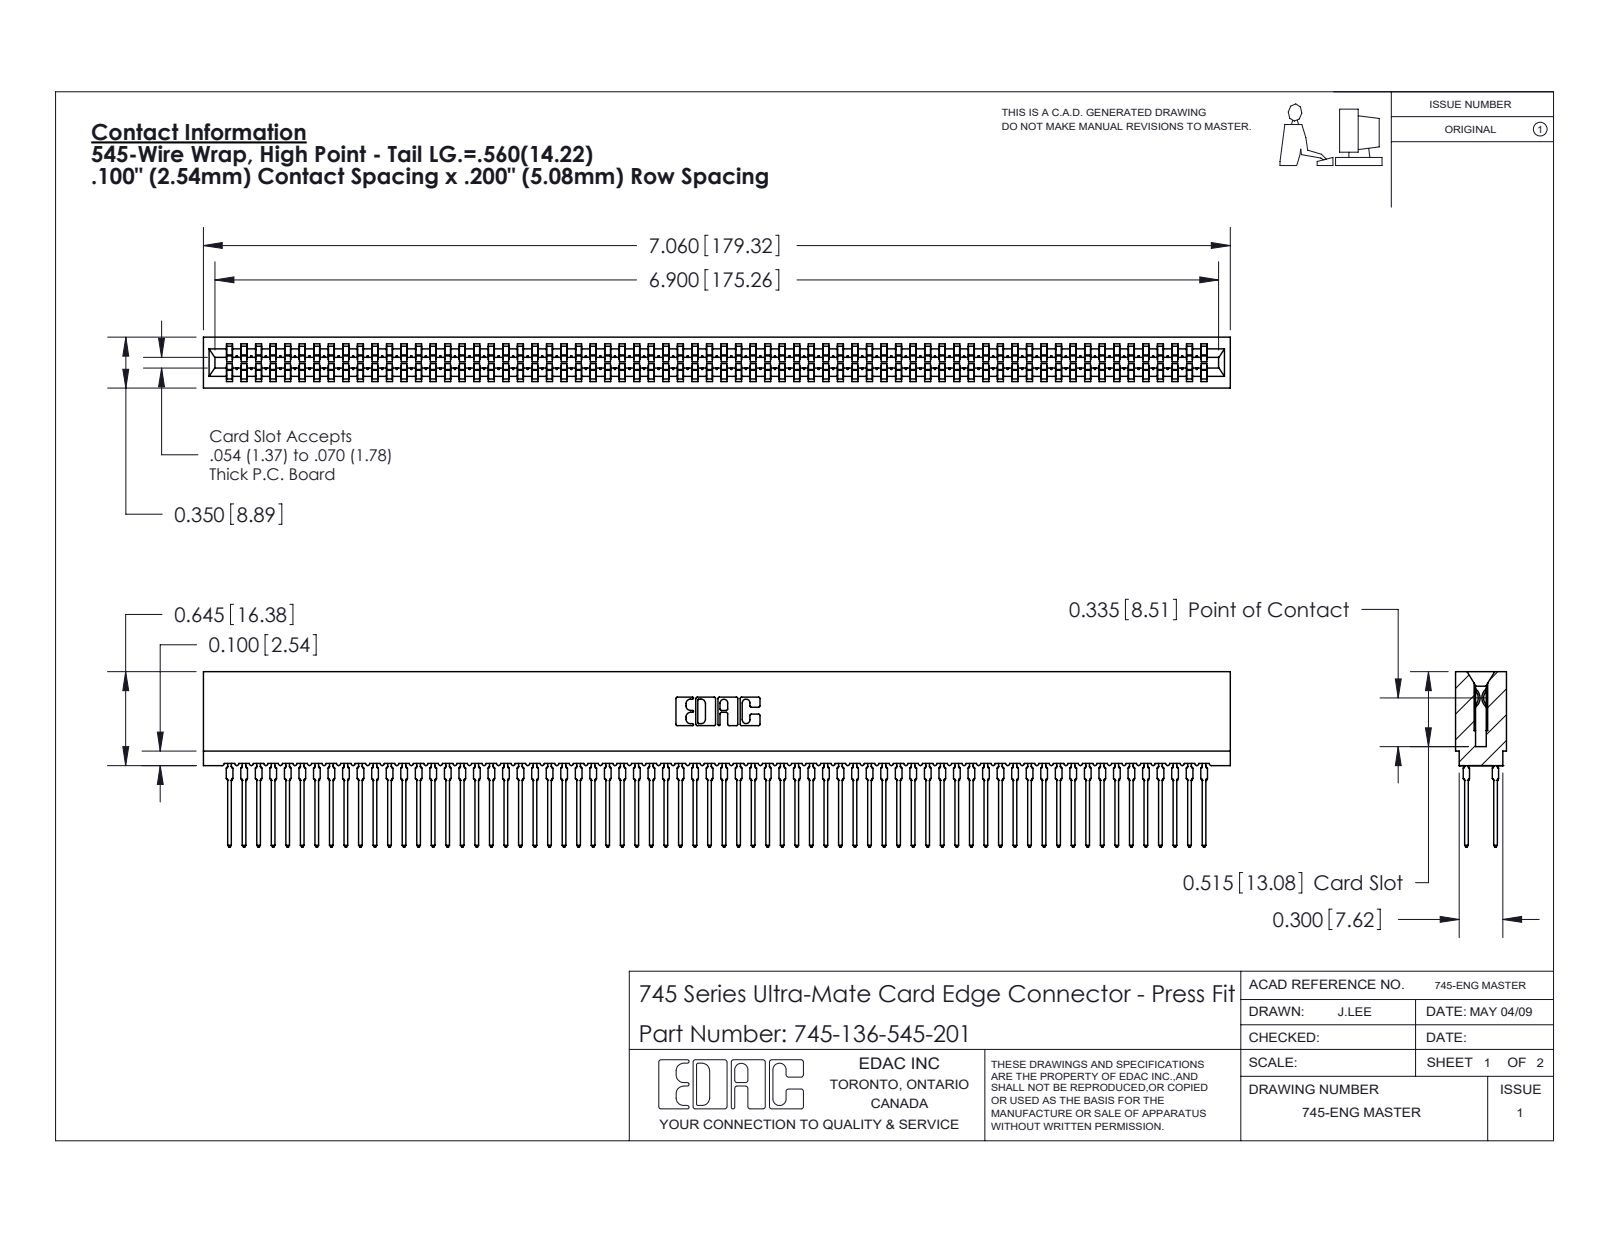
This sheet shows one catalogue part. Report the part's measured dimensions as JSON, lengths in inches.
{"part_name": "745 Part_Insulator Option - 01; 745-292-001_545; 745-136-545-201", "step_written_by": "SolidWorks 2020 (CONFIG_CONTROL_DESIGN)", "units": "inches", "bodies": {"solids": 137, "faces": 12267, "planar": 6311, "cylindrical": 2420, "other": 3536}, "overall_size": [7.06, 1.206, 0.35], "volume_in3": 1.005, "surface_area_in2": 56.05, "partial_cylinders_radius": [[0.021, 272], [0.015, 136], [0.01, 22], [0.005, 8], [0.011, 8], [0.007, 6], [0.031, 6], [0.026, 3]], "face_to_face_distances": [0.063, 0.287, 0.35, 0.045, 0.305, 0.018, 0.243, 0.138, 0.212, 0.093]}
